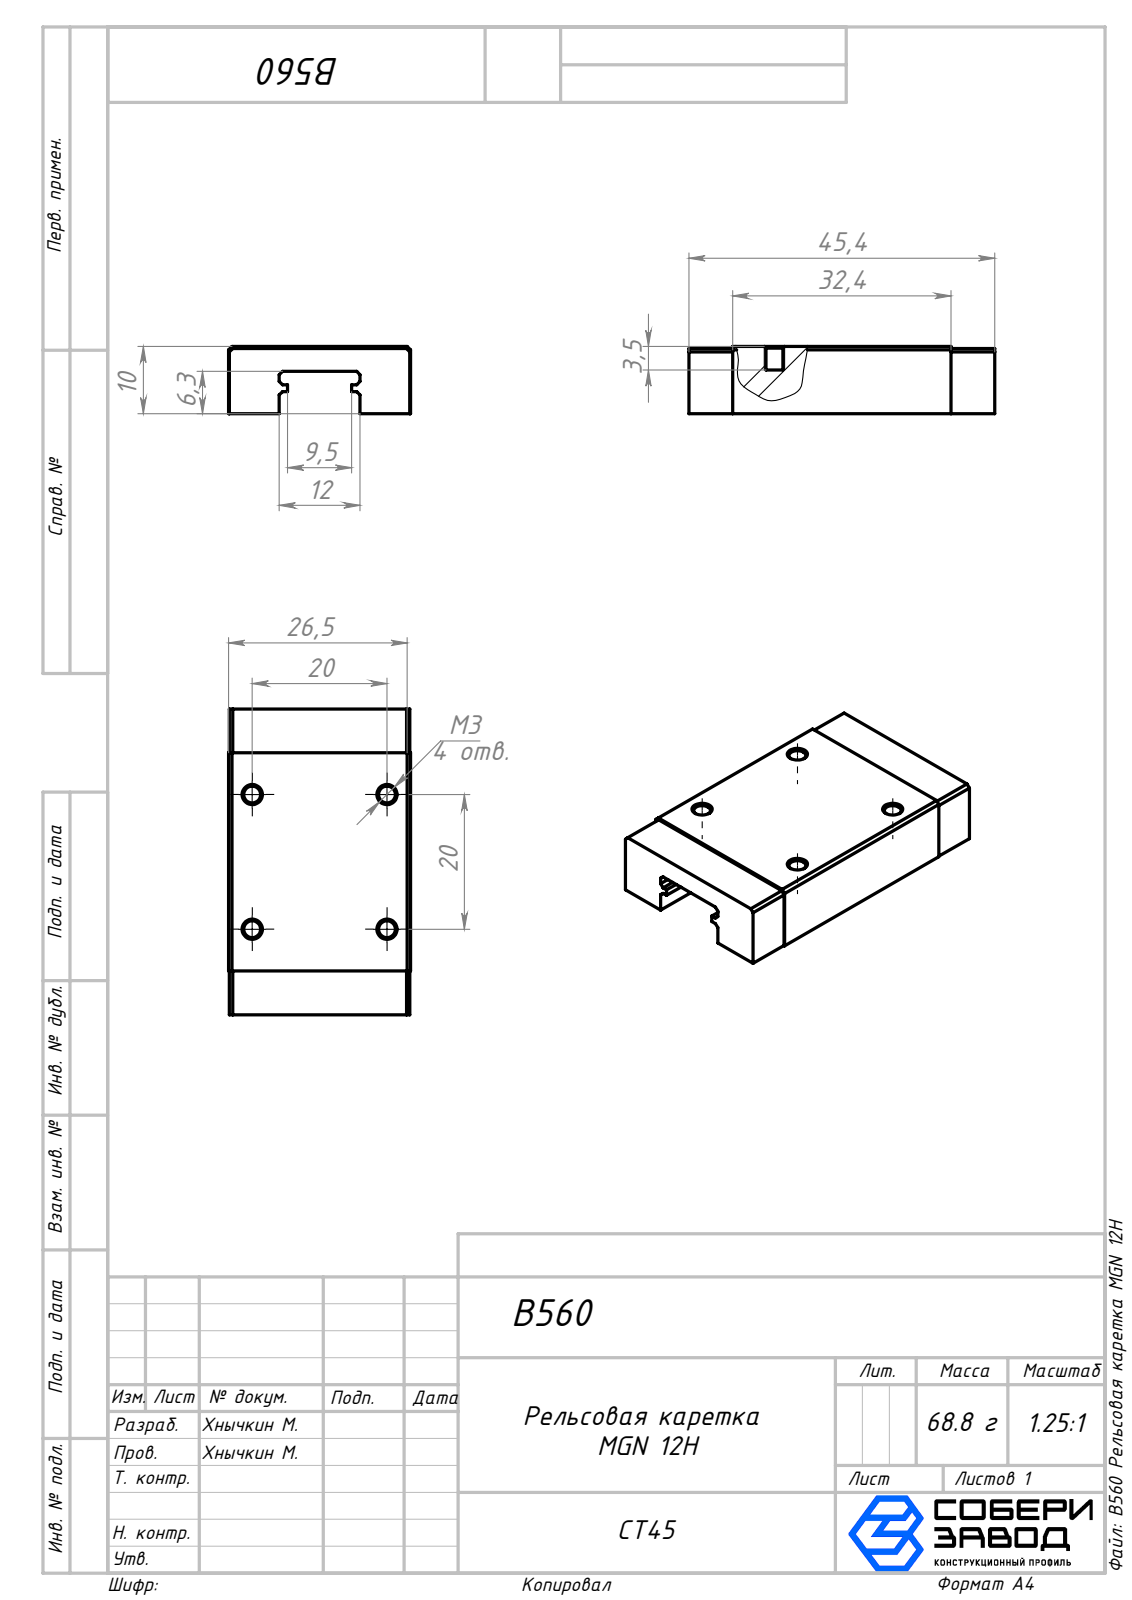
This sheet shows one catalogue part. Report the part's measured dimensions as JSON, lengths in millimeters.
{"part_name": "B560 Рельсовая каретка MGN 12H", "step_written_by": "SolidWorks 2026 (AUTOMOTIVE_DESIGN)", "units": "millimeters", "bodies": {"solids": 1, "faces": 58, "planar": 42, "cylindrical": 8, "other": 8}, "overall_size": [45.4, 27, 10], "volume_mm3": 8762, "surface_area_mm2": 4540, "round_holes": [[2.5, 4]], "face_to_face_distances": [10, 6.3, 3.7, 7.5, 19.5, 9.7, 3.4, 27, 26.9, 7.4], "hole_center_spacings": [20, 28.28]}
